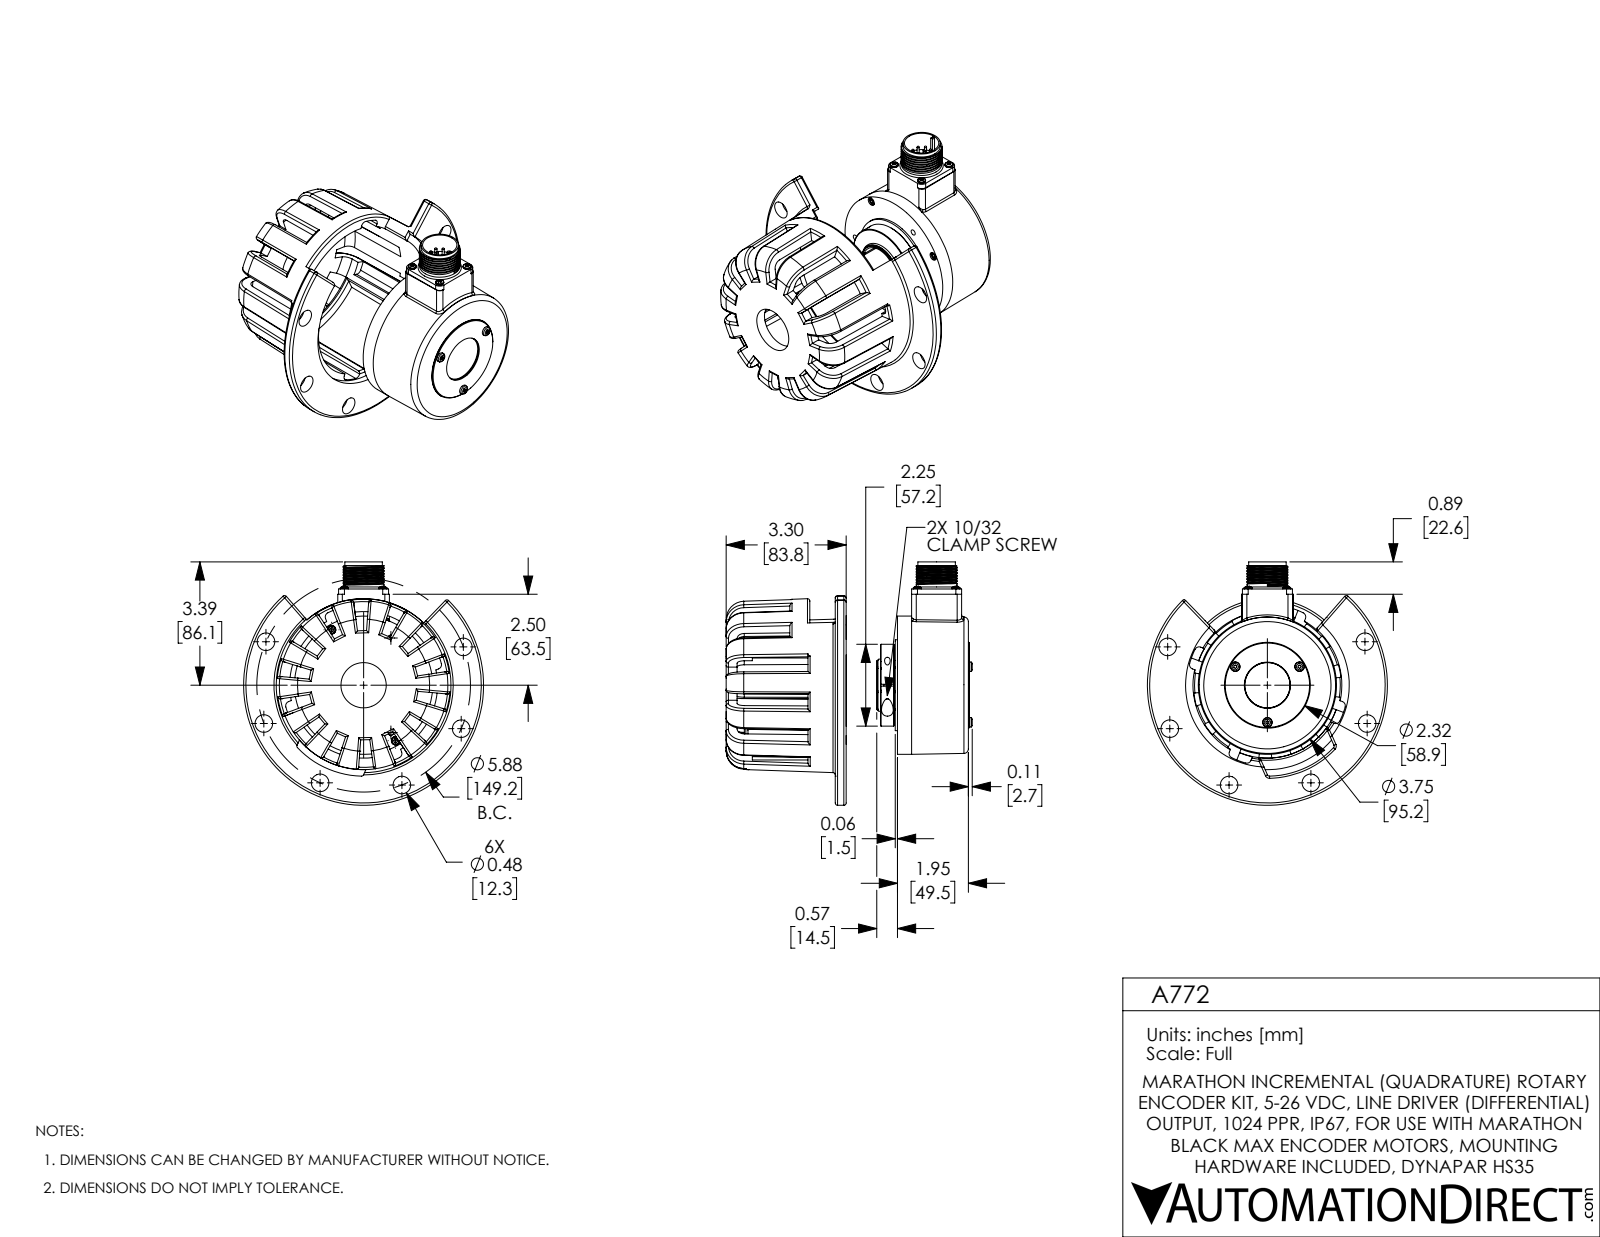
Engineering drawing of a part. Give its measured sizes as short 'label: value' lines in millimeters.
name: A772 fxt
written by: SolidWorks 2017 (AUTOMOTIVE_DESIGN)
unit: mm
bodies: 3 solids, 1282 faces (652 planar, 318 cylindrical, 312 other)
size: 171.8 × 170 × 167.6
volume: 560 100 mm³; area: 168 300 mm²
holes: 7× ⌀2.7, 6× ⌀12.3, 3× ⌀4, 2× ⌀4, 2× ⌀5.1, 2× ⌀8.3, 1× ⌀24, 1× ⌀31.6, 1× ⌀31.8, 1× ⌀32.3, 1× ⌀33, 1× ⌀35.6
bosses: 10× ⌀1.5, 4× ⌀5.6, 4× ⌀5.6, 3× ⌀3.5, 2× ⌀7.9, 2× ⌀4.8, 1× ⌀96.5, 1× ⌀79.2
rounds: 34× R1.6, 24× R1.5, 12× R3.2, 4× R4.1, 2× R0.8, 2× R9.5, 1× R16.9, 1× R56.4
face distances: 7.6, 76.2, 68.6, 83.8, 169.2, 161.5, 93, 85.3, 49.5, 119.6
hole spacings: 74.6, 105.5, 31.2, 44.9, 46.6, 57.1, 60.4, 113.8
